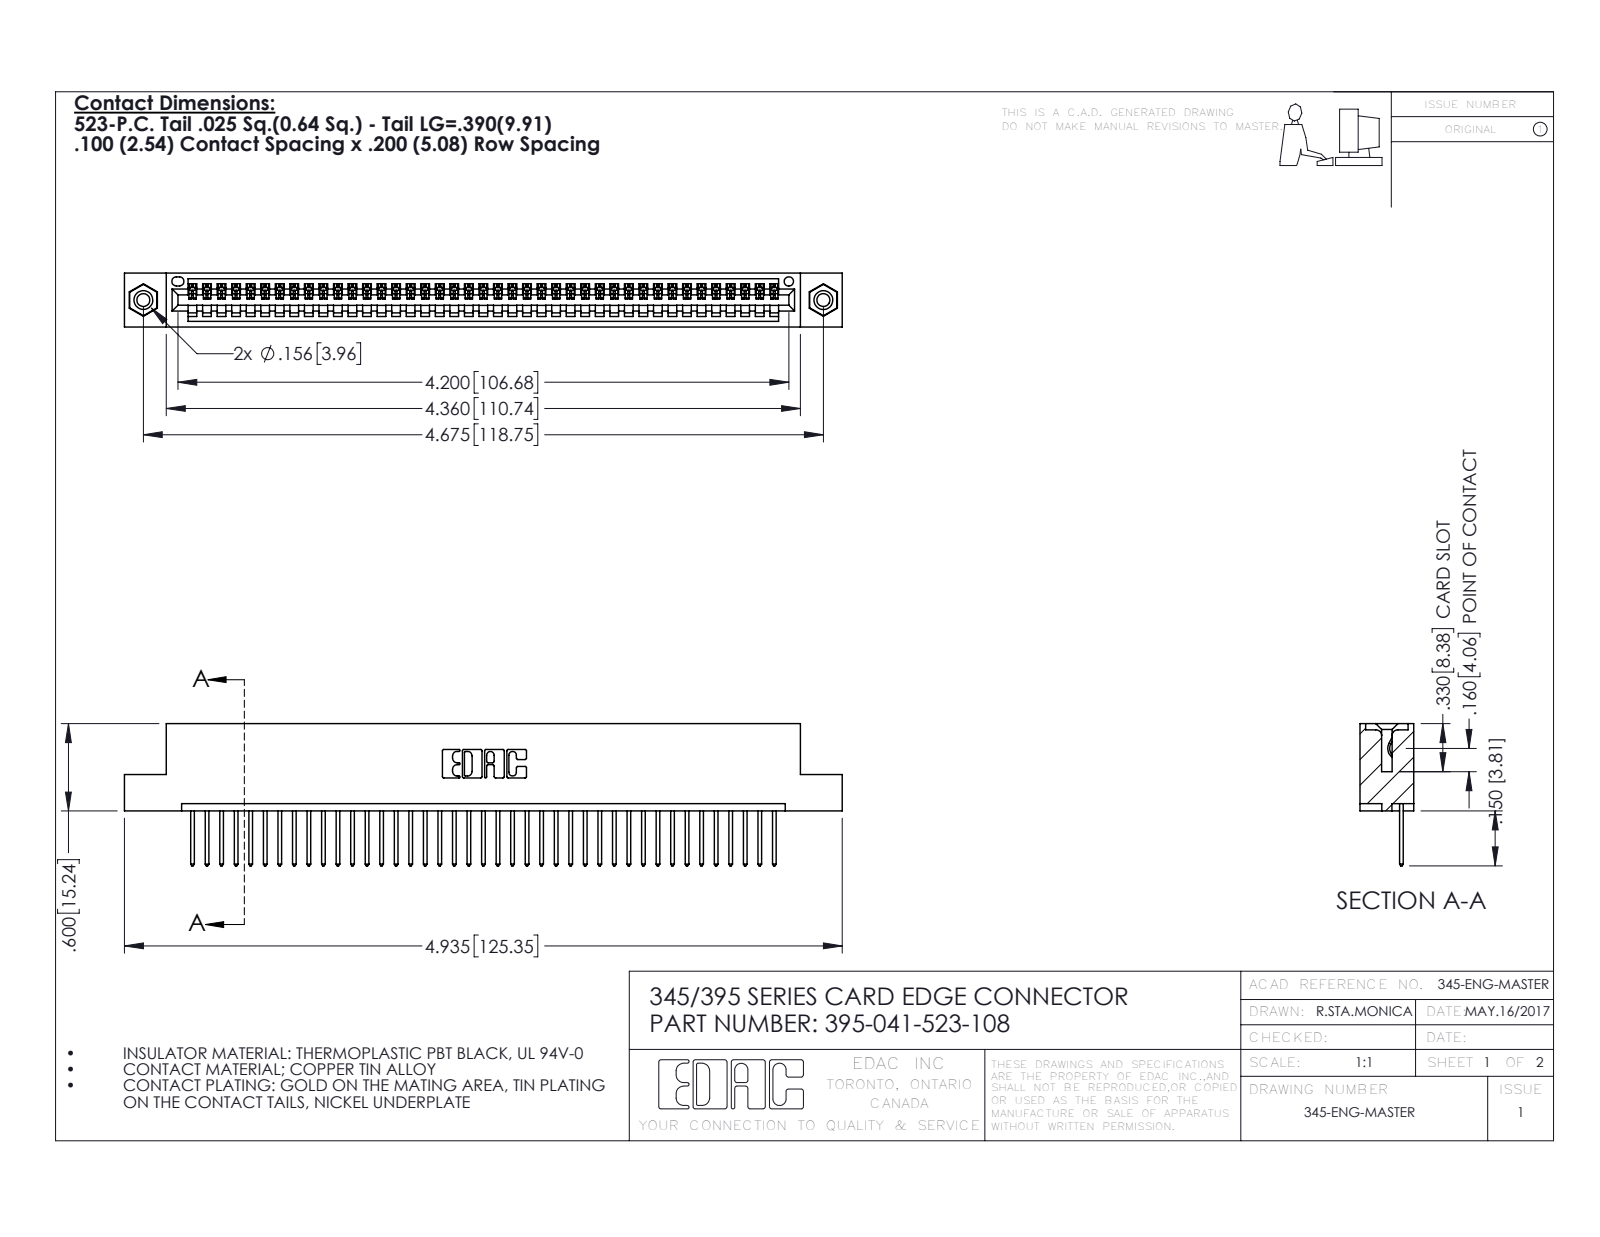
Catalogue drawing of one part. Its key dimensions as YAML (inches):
part_name: "345-250-001_345-250-003-102; 345 Part_Flush Mounting Lugs - 0.156 Dia-TI; 395-041-523-108; 345-292-001_345-293-123"
step_written_by: "SolidWorks 2016 (CONFIG_CONTROL_DESIGN)"
units: inches
bodies: {solids: 44, faces: 2564, planar: 1752, cylindrical: 796, other: 16}
overall_size: [4.935, 0.977, 0.37]
volume: 0.725
surface_area: 24.54
round_holes:
  - {diameter: 0.089, count: 2}
  - {diameter: 0.125, count: 2}
  - {diameter: 0.156, count: 2}
  - {diameter: 0.064, count: 1}
round_bosses_or_shafts:
  - {diameter: 0.155, count: 2}
partial_cylinders:
  - {radius: 0.006, count: 82}
  - {radius: 0.01, count: 82}
  - {radius: 0.01, count: 22}
  - {radius: 0.007, count: 6}
  - {radius: 0.031, count: 6}
  - {radius: 0.026, count: 3}
  - {radius: 0.031, count: 2}
  - {radius: 0.04, count: 2}
face_to_face_distances: [0.072, 0.298, 0.37, 0.2, 0.098, 0.272, 0.025, 0.225, 0.149, 0.072]
hole_center_spacings: [0.27, 4.439, 4.675]
